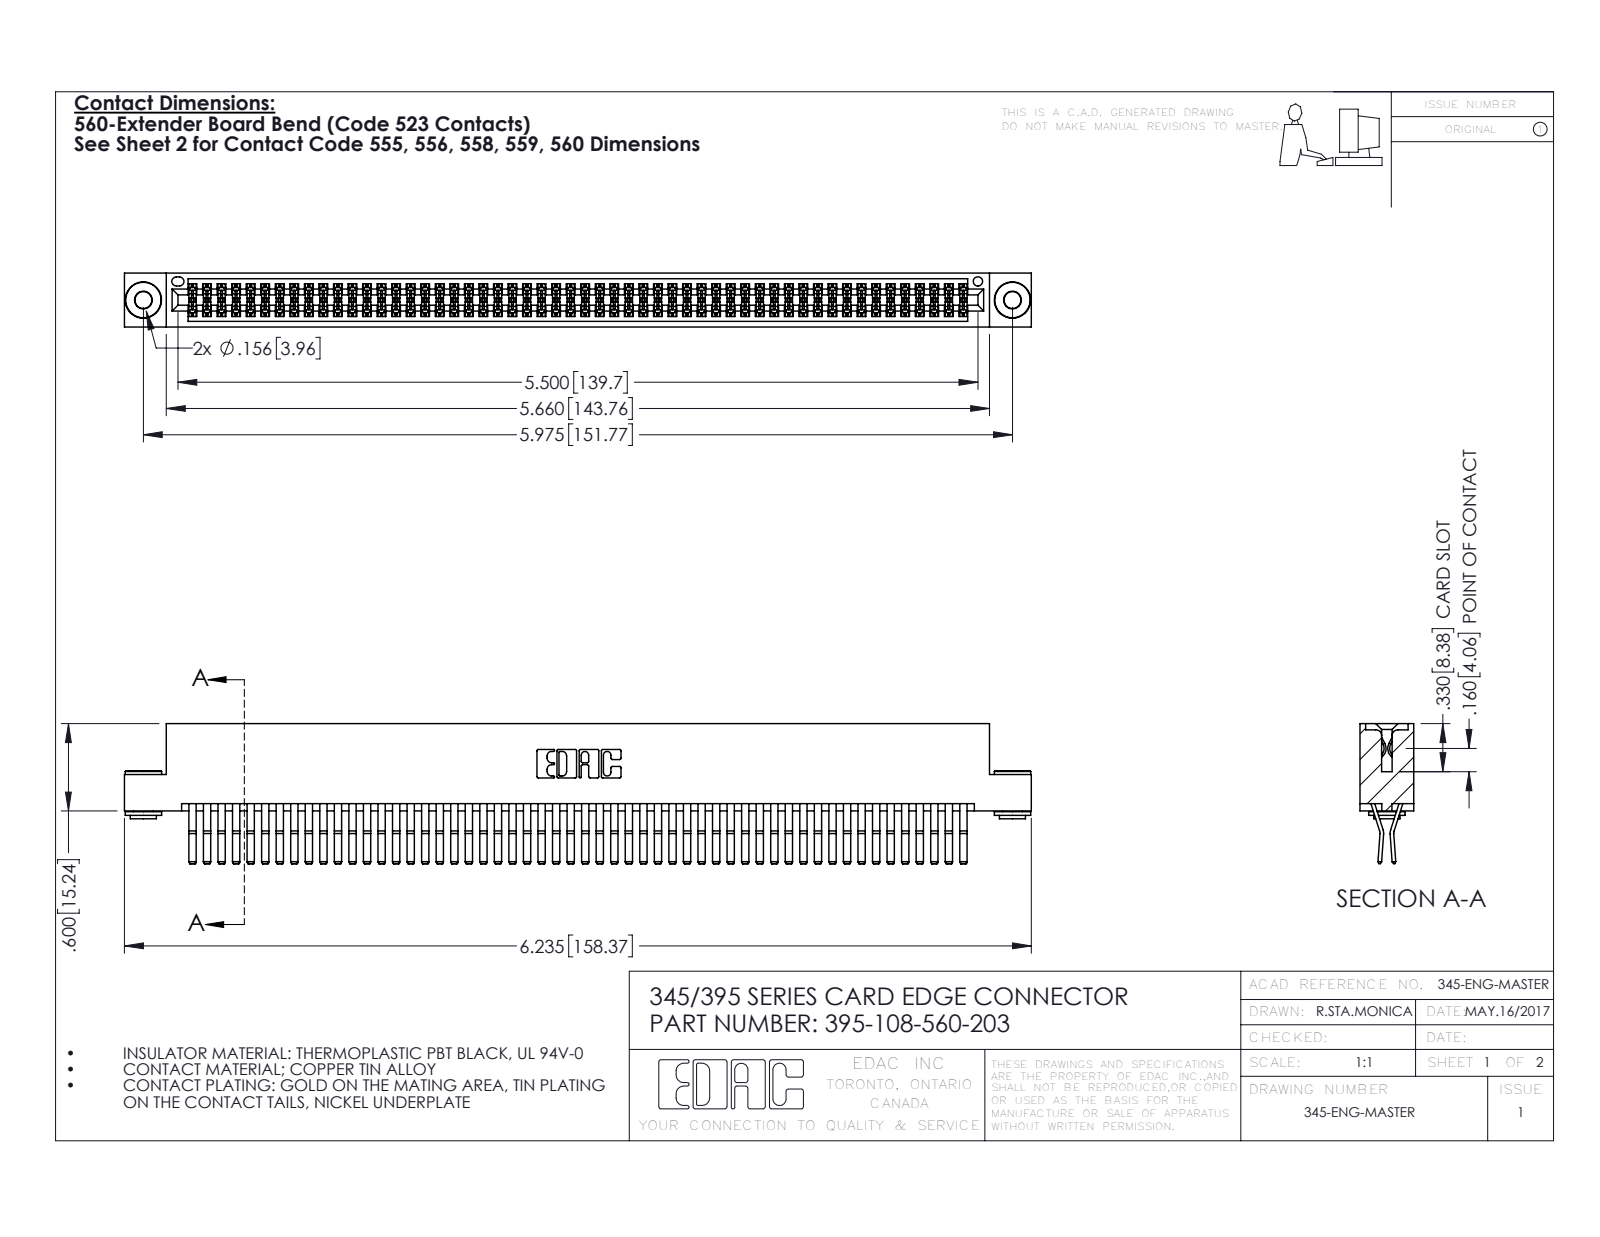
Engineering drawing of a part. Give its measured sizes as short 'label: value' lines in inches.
name: 345-292-001_560 Tail; 345-250-002_345-250-002-102; 395-108-560-203; 345 Part_Flush Mounting Lugs - 0.156 Dia-TH
written by: SolidWorks 2016 (CONFIG_CONTROL_DESIGN)
unit: in
bodies: 111 solids, 5780 faces (3654 planar, 2118 cylindrical, 8 other)
size: 6.235 × 0.962 × 0.37
volume: 0.99 in³; area: 40.67 in²
holes: 2× ⌀0.116, 2× ⌀0.156, 1× ⌀0.064
bosses: 2× ⌀0.25, 2× ⌀0.18, 2× ⌀0.136
rounds: 162× R0.006, 22× R0.01, 6× R0.007, 6× R0.031, 3× R0.026, 2× R0.01, 2× R0.014, 2× R0.019
face distances: 0.025, 0.072, 0.298, 0.37, 0.2, 0.098, 0.272, 0.225, 0.175, 0.149
hole spacings: 0.27, 5.739, 5.975
